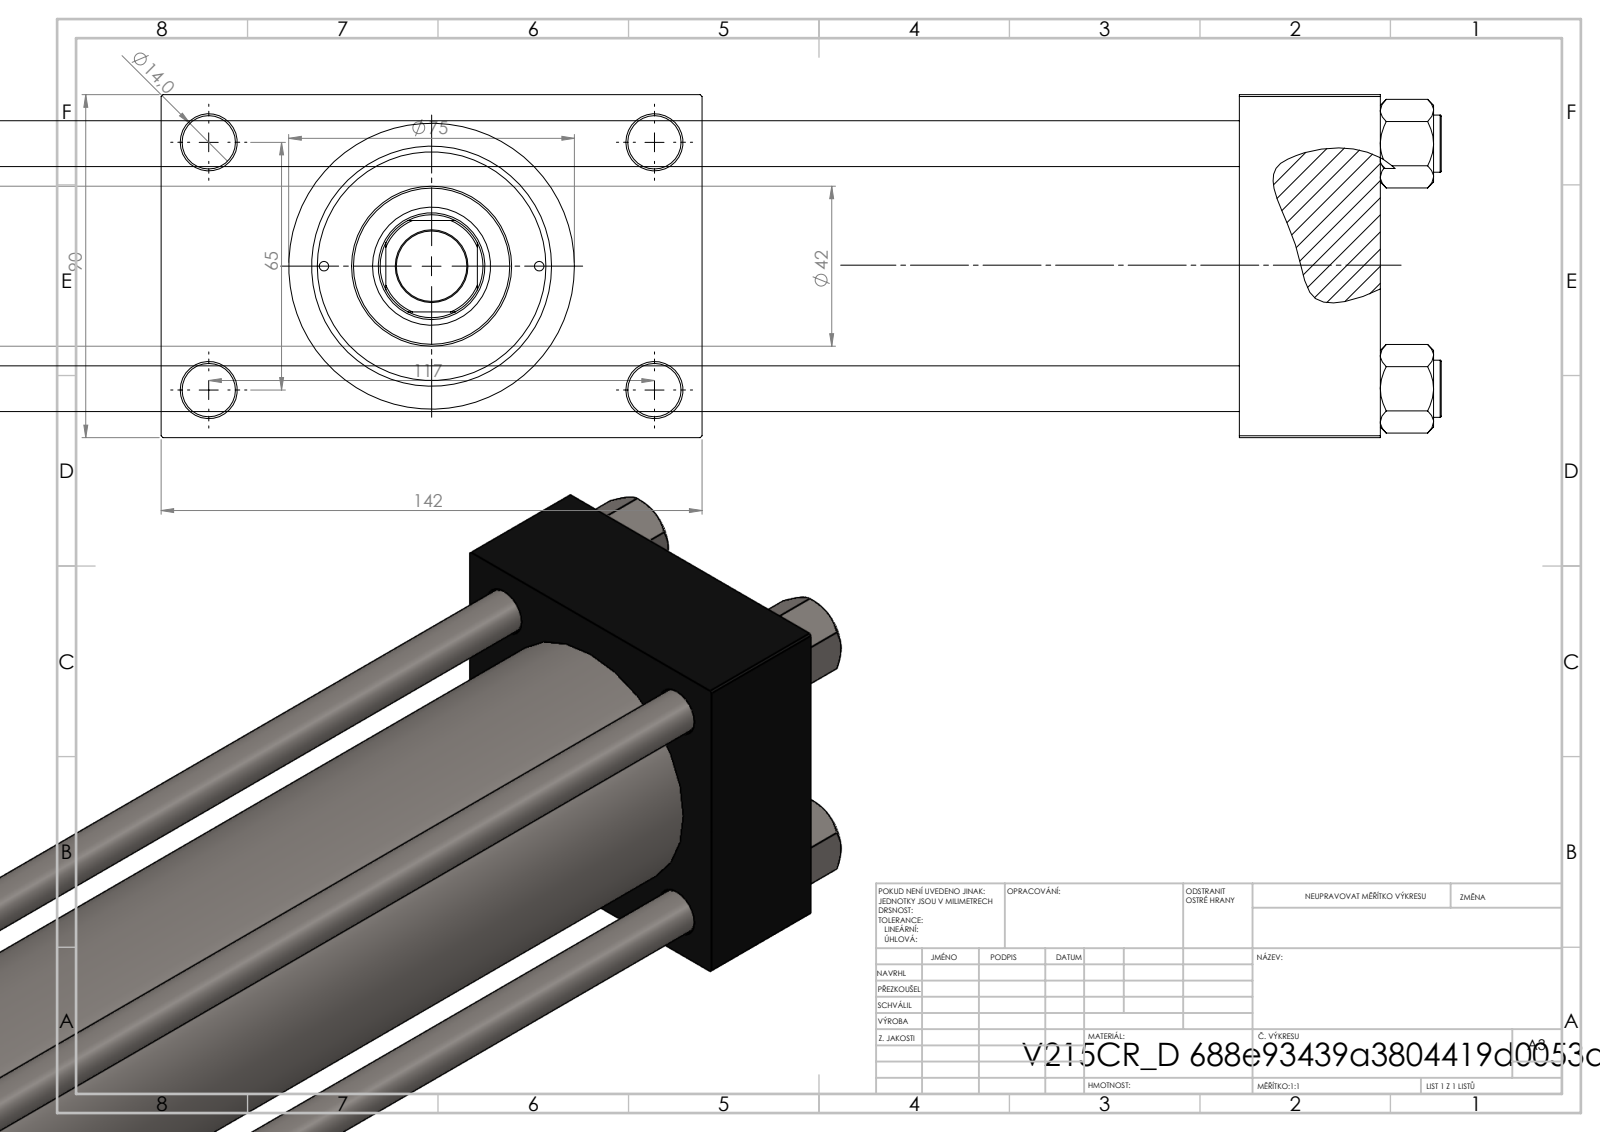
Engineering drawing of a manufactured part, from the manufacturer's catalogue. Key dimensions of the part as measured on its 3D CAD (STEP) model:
Part name (STEP PRODUCT): V215_VC_A; NUT_M5_D; V215CR_D_Body; V215CR_VCP_D (+1 more)
STEP written by: SolidWorks 2019 (CONFIG_CONTROL_DESIGN)
Units: millimetres
Bodies: 11 solids, 1111 faces (499 planar, 92 cylindrical, 520 other)
Overall size (bounding box): 583 × 142 × 90
Volume: 1 738 000 mm³ · Surface area: 448 541 mm²
Round holes (diameter × count): ⌀12 ×4, ⌀14 ×4, ⌀2.5 ×2, ⌀7 ×2, ⌀20.96 ×2, ⌀30 ×2, ⌀18.5 ×1, ⌀28 ×1, ⌀31 ×1, ⌀50 ×1, ⌀60 ×1, ⌀63 ×1
Round bosses / shafts (diameter × count): ⌀15 ×4, ⌀75 ×1, ⌀69 ×1, ⌀42 ×1
Partial cylindrical surfaces — rounded edges, fillets, slot ends (radius × count): R13.5 ×1
Main face-to-face distances: 90, 439, 37, 476, 483, 520, 44, 26, 116, 16
Hole centre spacings: 26.35, 32.39, 44.4, 45.47, 64.3, 66.92, 68.42, 69.81
